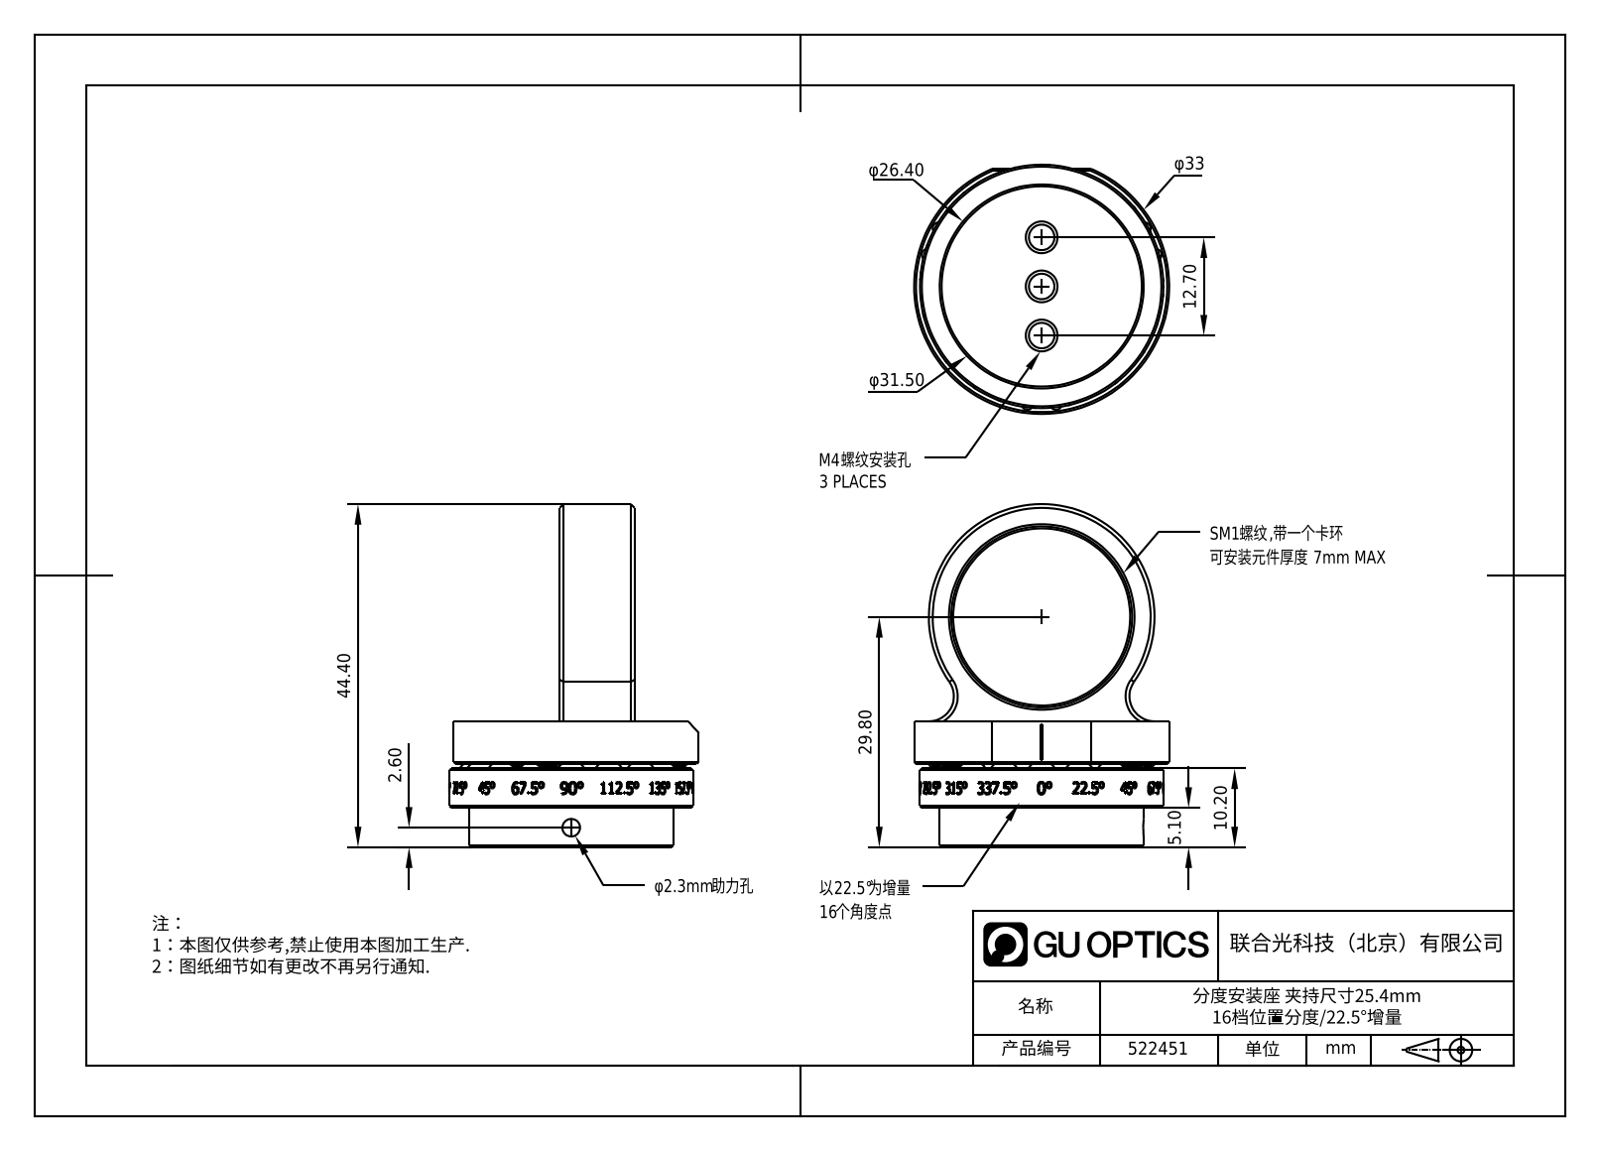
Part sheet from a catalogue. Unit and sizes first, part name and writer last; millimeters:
Units: millimetres
Overall size (bounding box): 44.41 × 33 × 32.25
Round holes (diameter × count): ⌀3.3 ×3, ⌀2.3 ×1, ⌀22.9 ×1, ⌀24 ×1, ⌀25.69 ×1, ⌀26.69 ×1, ⌀27.5 ×1
Round bosses / shafts (diameter × count): ⌀1.5 ×2, ⌀33 ×1, ⌀31.5 ×1, ⌀26.4 ×1, ⌀26.29 ×1
Partial cylindrical surfaces — rounded edges, fillets, slot ends (radius × count): R0.75 ×6, R3.24 ×2, R14.6 ×1, R15 ×1, R15.72 ×1
Main face-to-face distances: 16.3, 5.1, 10.2, 6.1, 11.2, 10.8, 5.7, 0.6, 5.5, 9.7
Hole centre spacings: 6.35, 12.7
Bodies: 0 solids, 447 faces (95 planar, 149 cylindrical, 203 other)
Part name (STEP PRODUCT): 1.3.7.2_ZZF-16NX1.0_16档位分度安装座，用于?1英寸光学元件，M4螺纹
STEP written by: SolidWorks 2021 (CONFIG_CONTROL_DESIGN)
